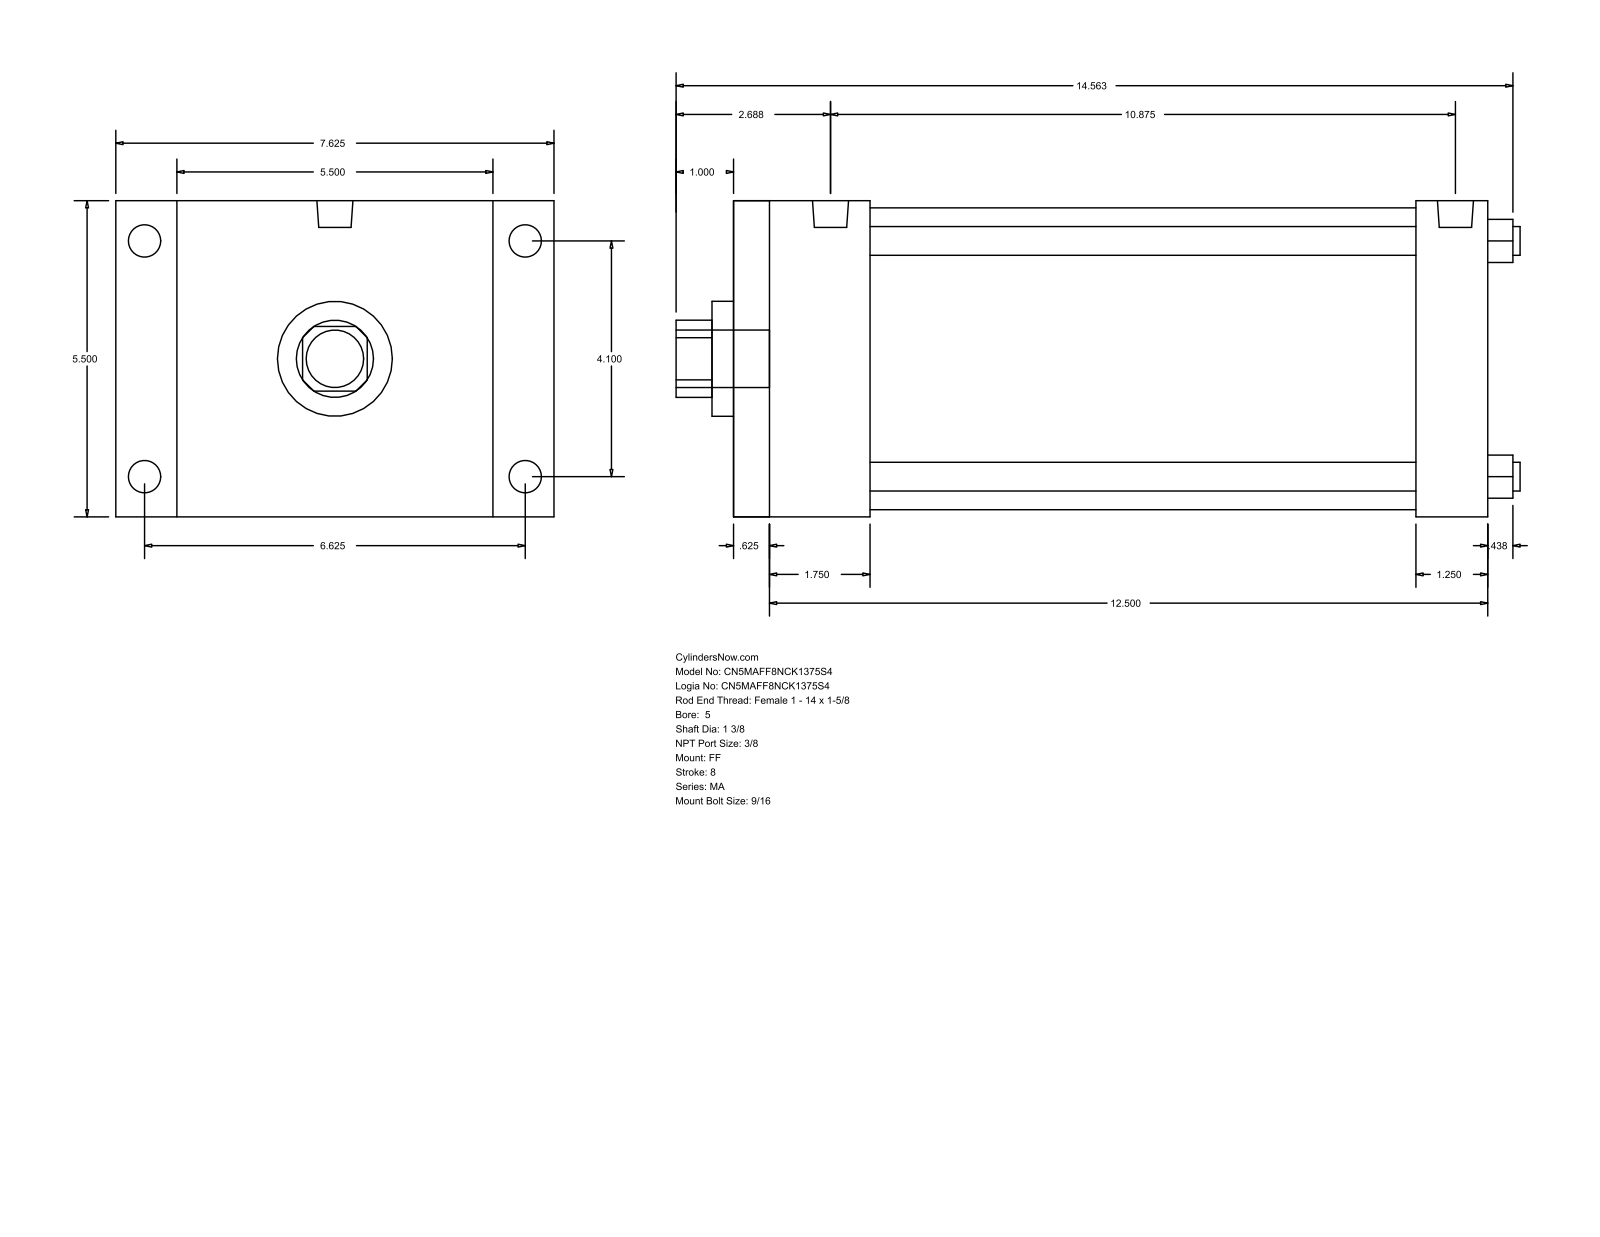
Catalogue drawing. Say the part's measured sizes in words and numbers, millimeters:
The part is named "MA_FF__0500_1.375". Its 3-D file was written by "GSSL Pune (CONFIG_CONTROL_DESIGN)". It is 0 solids with 92 faces: 64 planar, 28 cylindrical and 0 other. Overall it measures 373.06 by 193.68 by 139.7 millimeters. Round holes: 4 of diameter 12.7, 1 of diameter 34.92, 1 of diameter 50.8, 1 of diameter 133.35. Round bosses or shafts: 4 of diameter 14.29, 4 of diameter 11.11, 2 of diameter 15.93, 1 of diameter 25.4. Partial cylindrical surfaces (rounded edges, fillets, slot ends): 1 of radius 17.06. The main face-to-face distances are 139.7, 333.37, 15.87, 317.5, 301.62, 285.75, 31.75, 60.32, 44.45, 241.3. The hole center spacings are 73.64, 104.14, 147.28.
